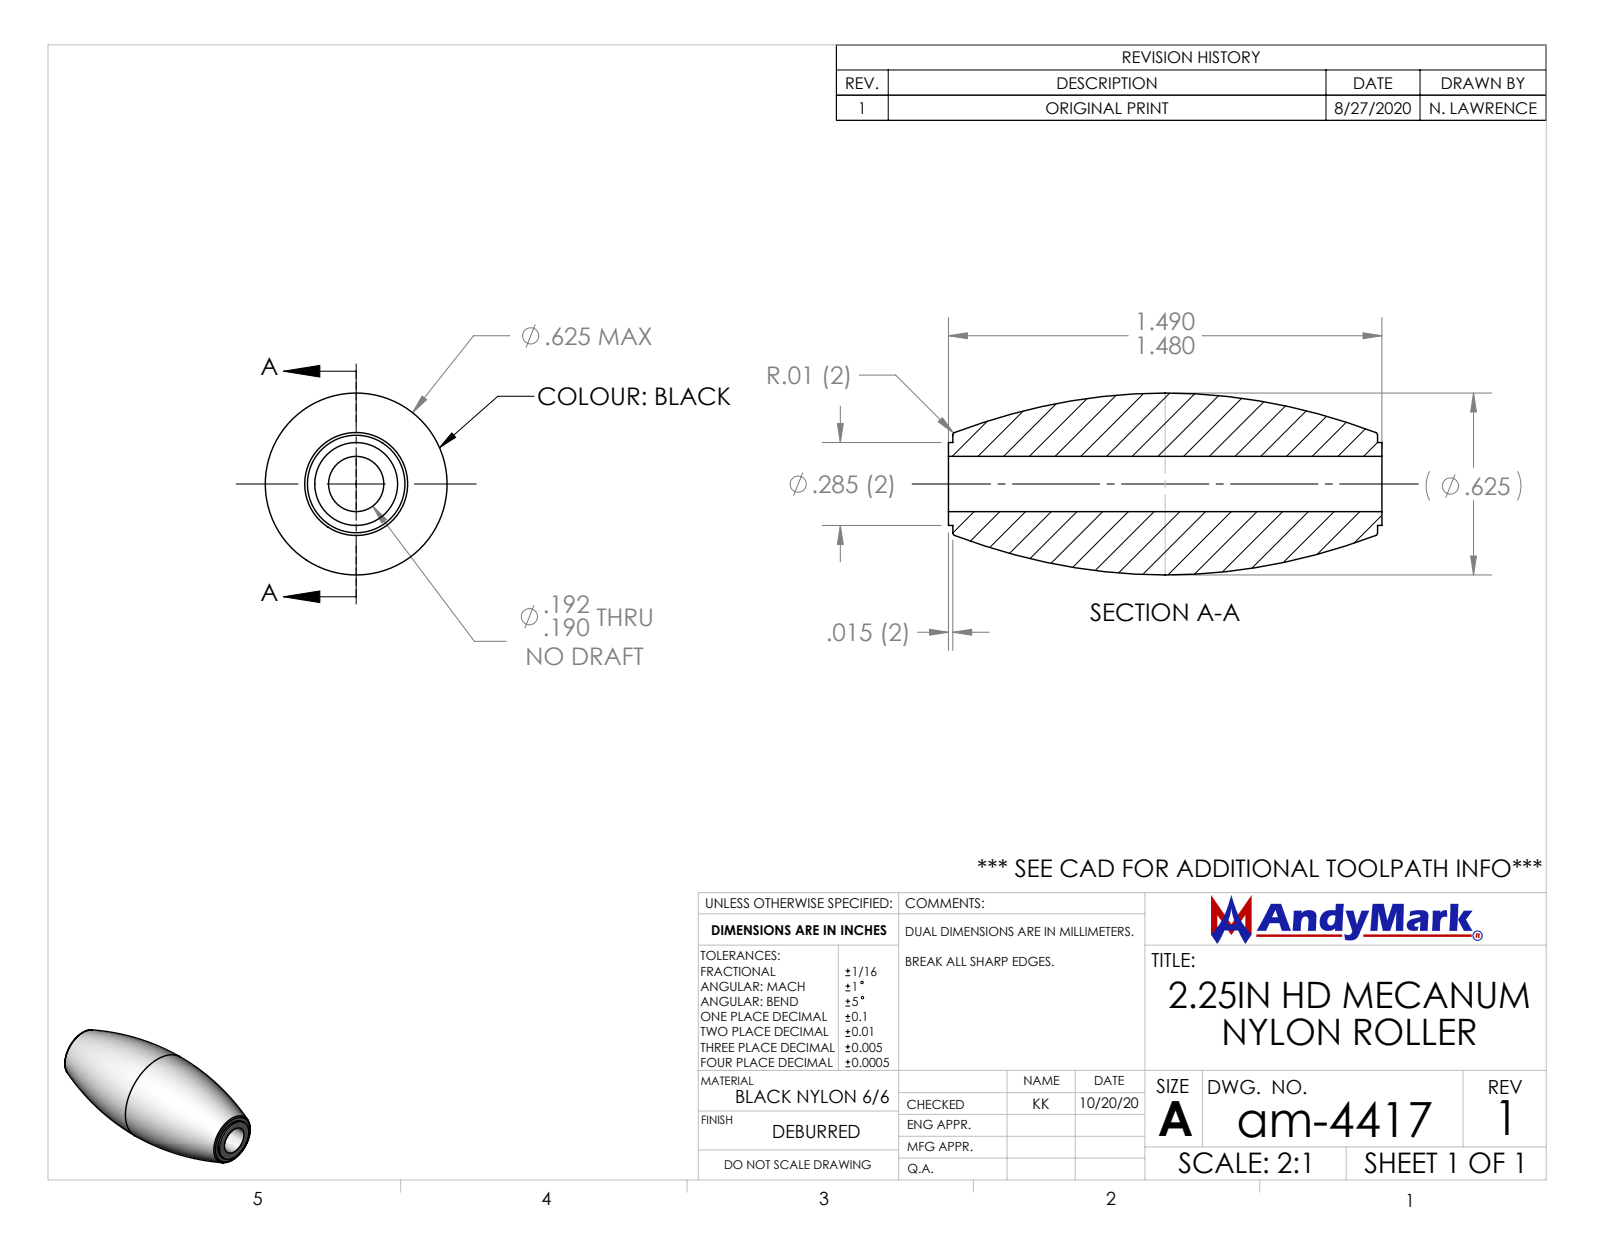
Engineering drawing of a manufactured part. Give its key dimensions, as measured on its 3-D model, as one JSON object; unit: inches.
{"part_name": "am-4417 2.25IN HD Mecanum Nylon Roller", "step_written_by": "SolidWorks 2019 (AUTOMOTIVE_DESIGN)", "units": "inches", "bodies": {"solids": 1, "faces": 11, "planar": 4, "cylindrical": 3, "other": 4}, "overall_size": [1.49, 0.625, 0.625], "volume_in3": 0.293, "surface_area_in2": 3.542, "round_holes": [[0.19, 1]], "round_bosses_or_shafts": [[0.285, 1]], "face_to_face_distances": [0.015, 1.475, 1.49, 1.46]}
